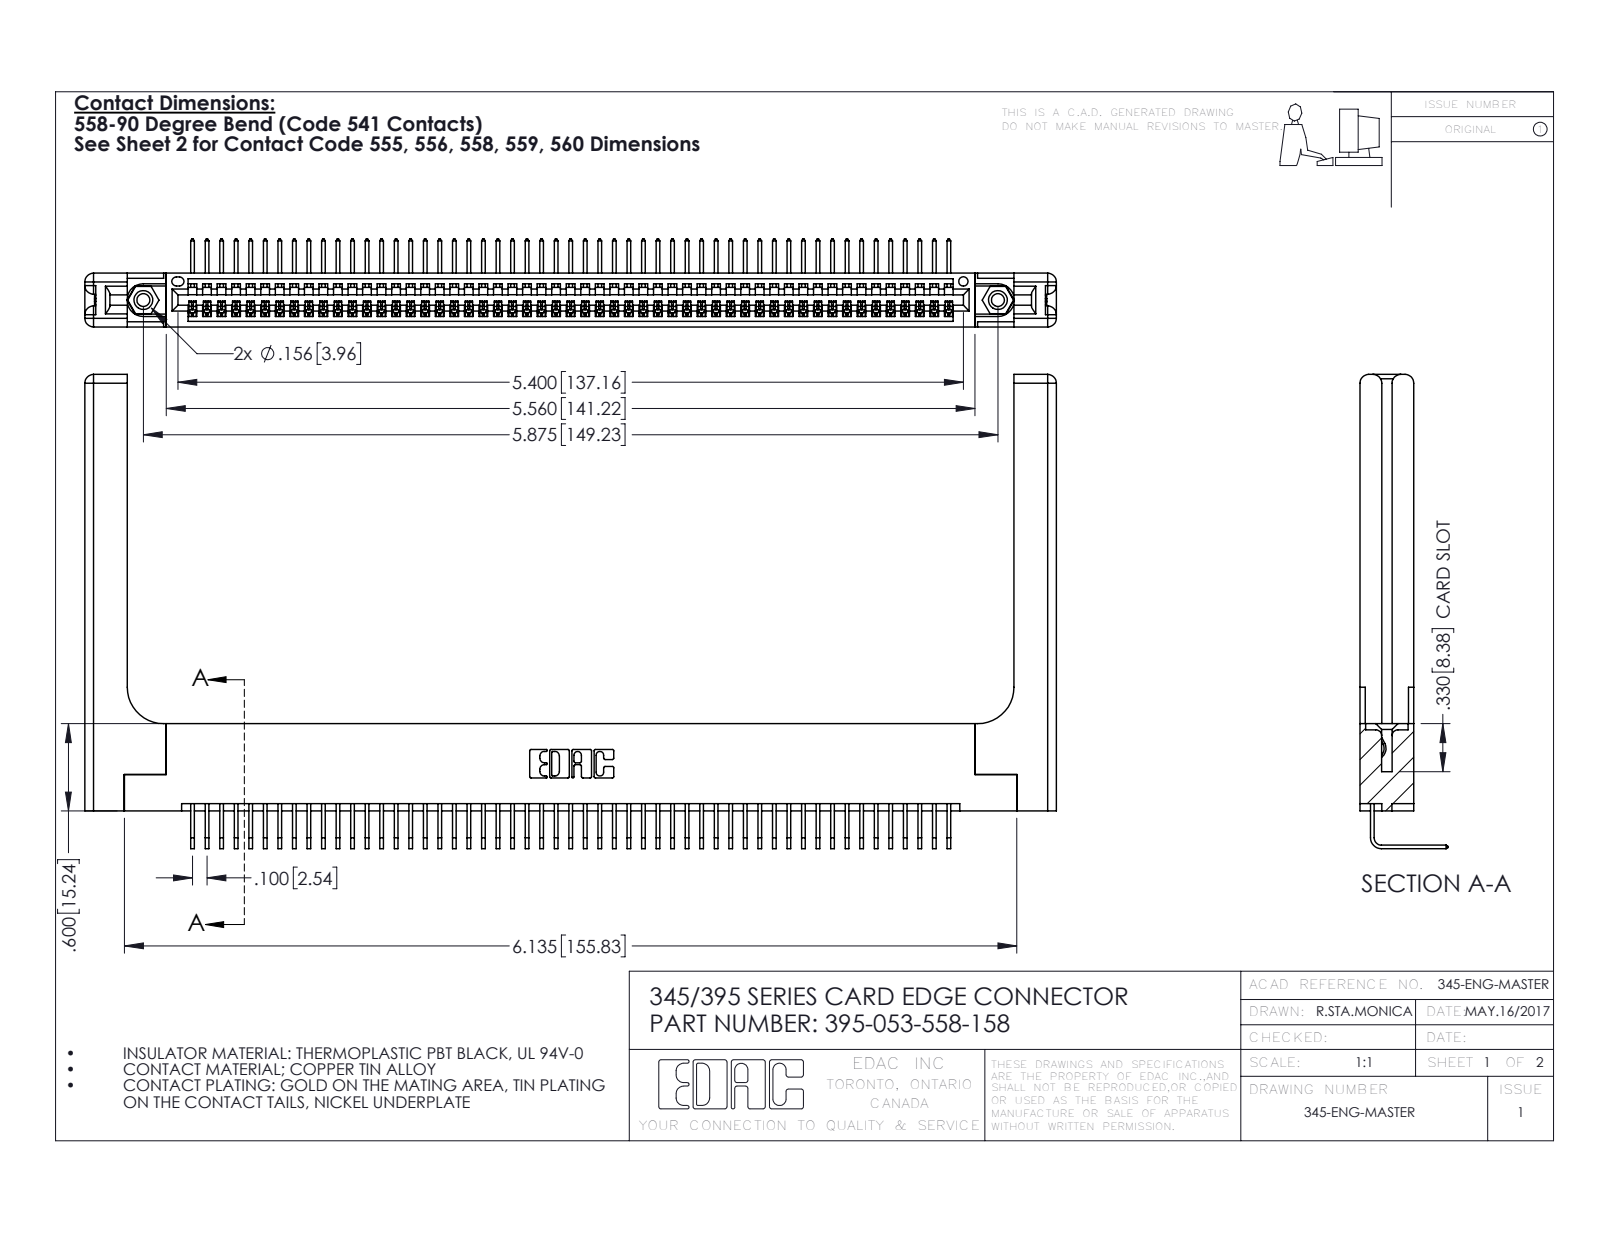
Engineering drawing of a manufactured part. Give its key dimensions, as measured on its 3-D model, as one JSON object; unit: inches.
{"part_name": "345-292-001_558 Tail - 2; 345 Part_Flush Mounting Lugs - 0.156 Dia-TH; 345-220-058_345-220-058; 395-053-558-158 (+1 more)", "step_written_by": "SolidWorks 2016 (CONFIG_CONTROL_DESIGN)", "units": "inches", "bodies": {"solids": 58, "faces": 3562, "planar": 2454, "cylindrical": 1048, "other": 60}, "overall_size": [6.679, 3.259, 0.605], "volume_in3": 1.519, "surface_area_in2": 43.8, "round_holes": [[0.089, 2], [0.125, 2], [0.156, 2], [0.064, 1]], "round_bosses_or_shafts": [[0.155, 2]], "partial_cylinders_radius": [[0.006, 106], [0.01, 22], [0.06, 16], [0.007, 6], [0.031, 6], [0.026, 3], [0.03, 2], [0.031, 2]], "face_to_face_distances": [0.072, 0.37, 0.298, 0.2, 0.098, 0.272, 0.025, 0.225, 0.148, 0.15], "hole_center_spacings": [0.27, 5.639, 5.875]}
